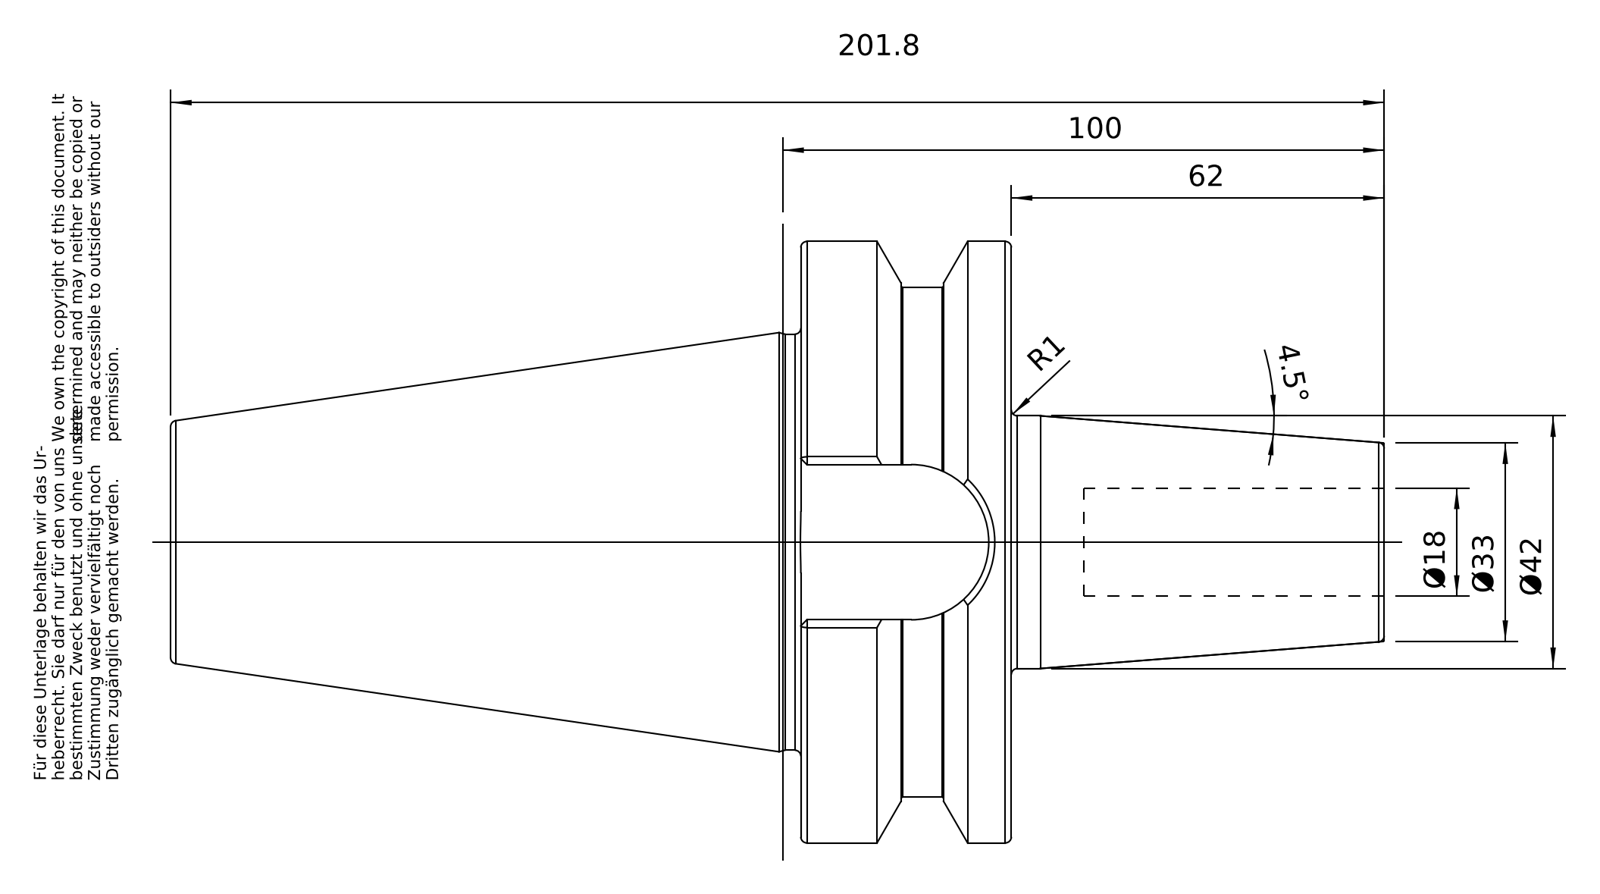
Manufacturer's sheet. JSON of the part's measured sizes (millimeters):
{"part_name": "50-640-18", "step_written_by": "PRO/ENGINEER BY PARAMETRIC TECHNOLOGY CORPORATION, 2010430 (CONFIG_CONTROL_DESIGN)", "units": "millimeters", "bodies": {"solids": 1, "faces": 96, "planar": 26, "cylindrical": 22, "other": 48}, "overall_size": [201.8, 99.97, 99.97], "volume_mm3": 525469, "surface_area_mm2": 61445, "round_holes": [[18, 1], [20.75, 1], [25.02, 1], [25.7, 1]], "round_bosses_or_shafts": [[99.97, 1], [84.75, 1], [69.15, 1], [42, 1], [24.01, 1]], "partial_cylinders_radius": [[12.9, 1]], "face_to_face_distances": [35, 70.4, 97, 62, 104.8, 139.8, 201.8, 25.8, 151.8, 47]}
